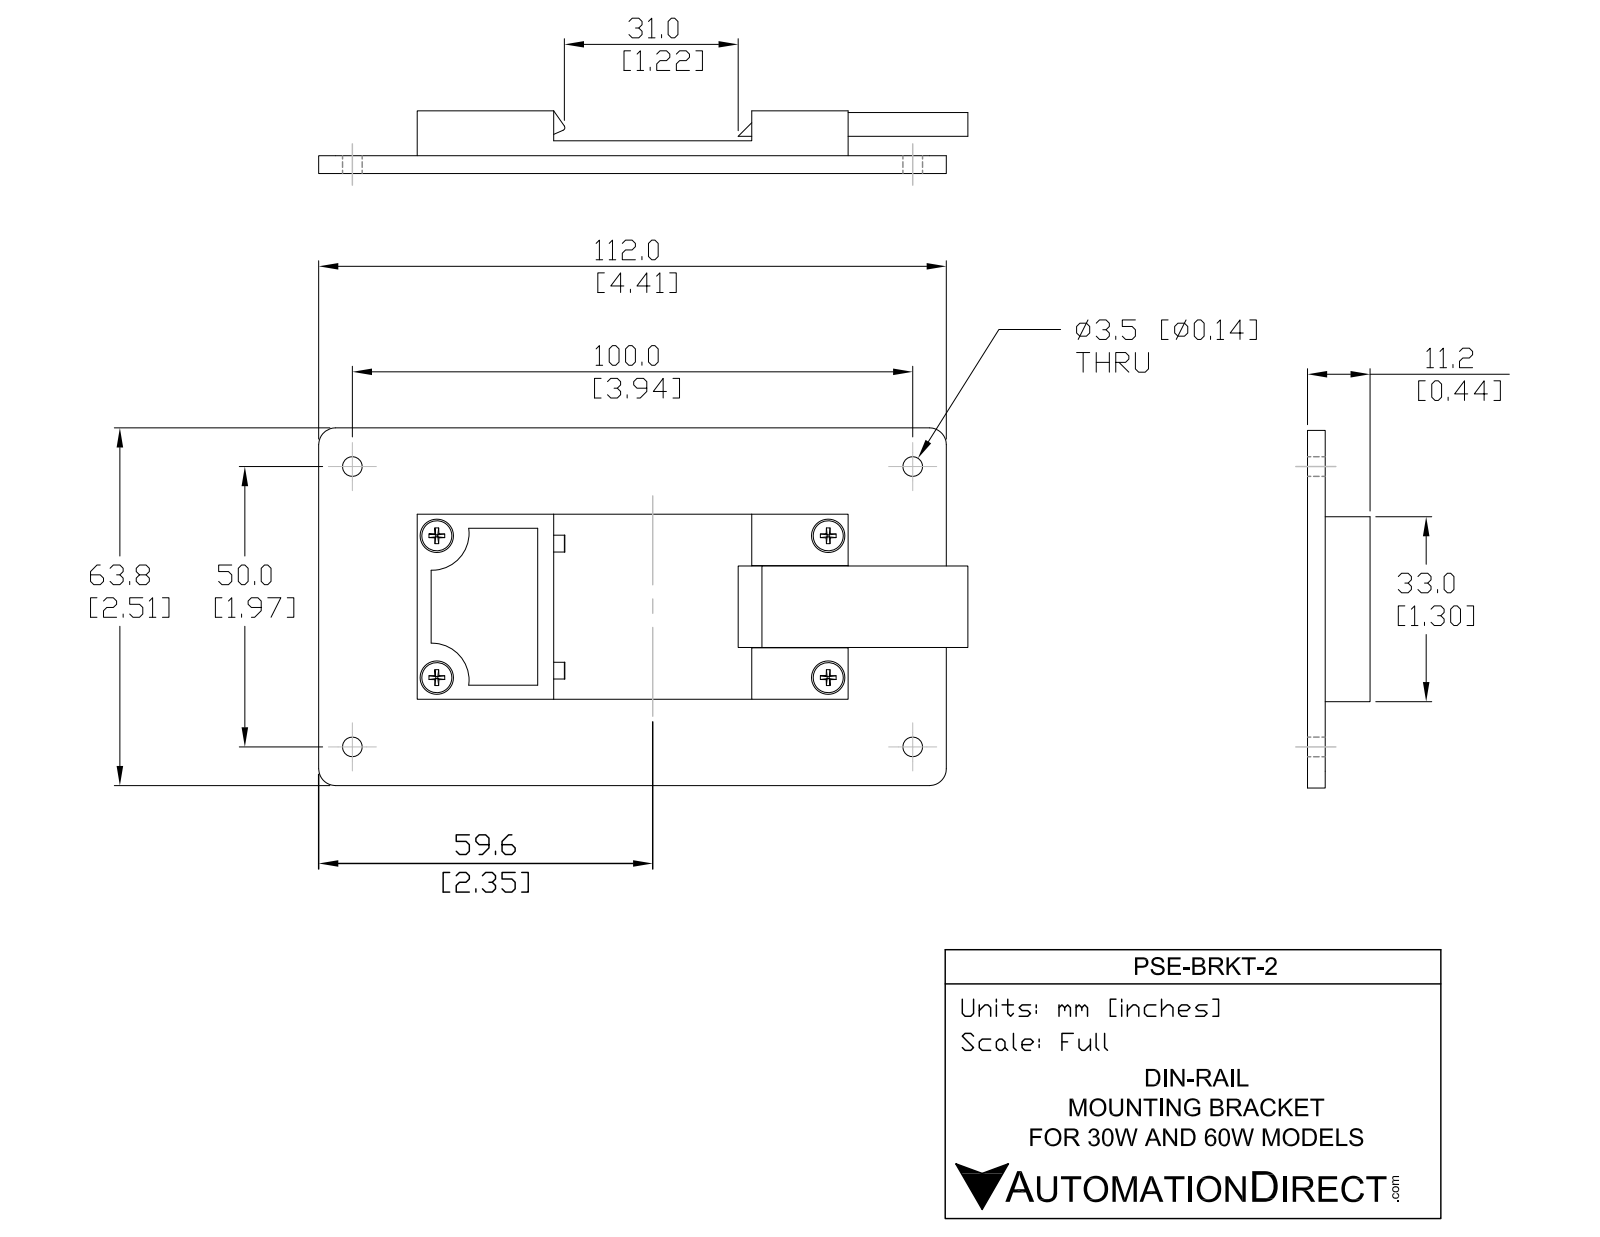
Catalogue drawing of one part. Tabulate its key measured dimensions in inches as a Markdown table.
| quantity | value |
| --- | --- |
| part name | PSE-BRKT-2 |
| STEP written by | SolidWorks 2011 (CONFIG_CONTROL_DESIGN) |
| units | inches |
| bodies | 1 solid, 177 faces (123 planar, 36 cylindrical, 18 other) |
| overall size | 4.56 × 2.51 × 0.44 |
| volume | 2.111 in³ |
| surface area | 30.57 in² |
| round holes (diameter × count) | 0.14 × 4, 0.23 × 4 |
| round bosses / shafts (diameter × count) | 0.199 × 4 |
| partial cylindrical surfaces (radius × count) | 0.125 × 4, 0.26 × 2, 0.015 × 1 |
| main face-to-face distances | 0.125, 0.105, 0.23, 0.605, 1.905, 0.2, 0.44, 0.315, 0.21, 0.1 |
| hole center spacings | 0.768, 1, 1.6, 1.6, 1.97, 2.75, 2.926, 3.38 |
